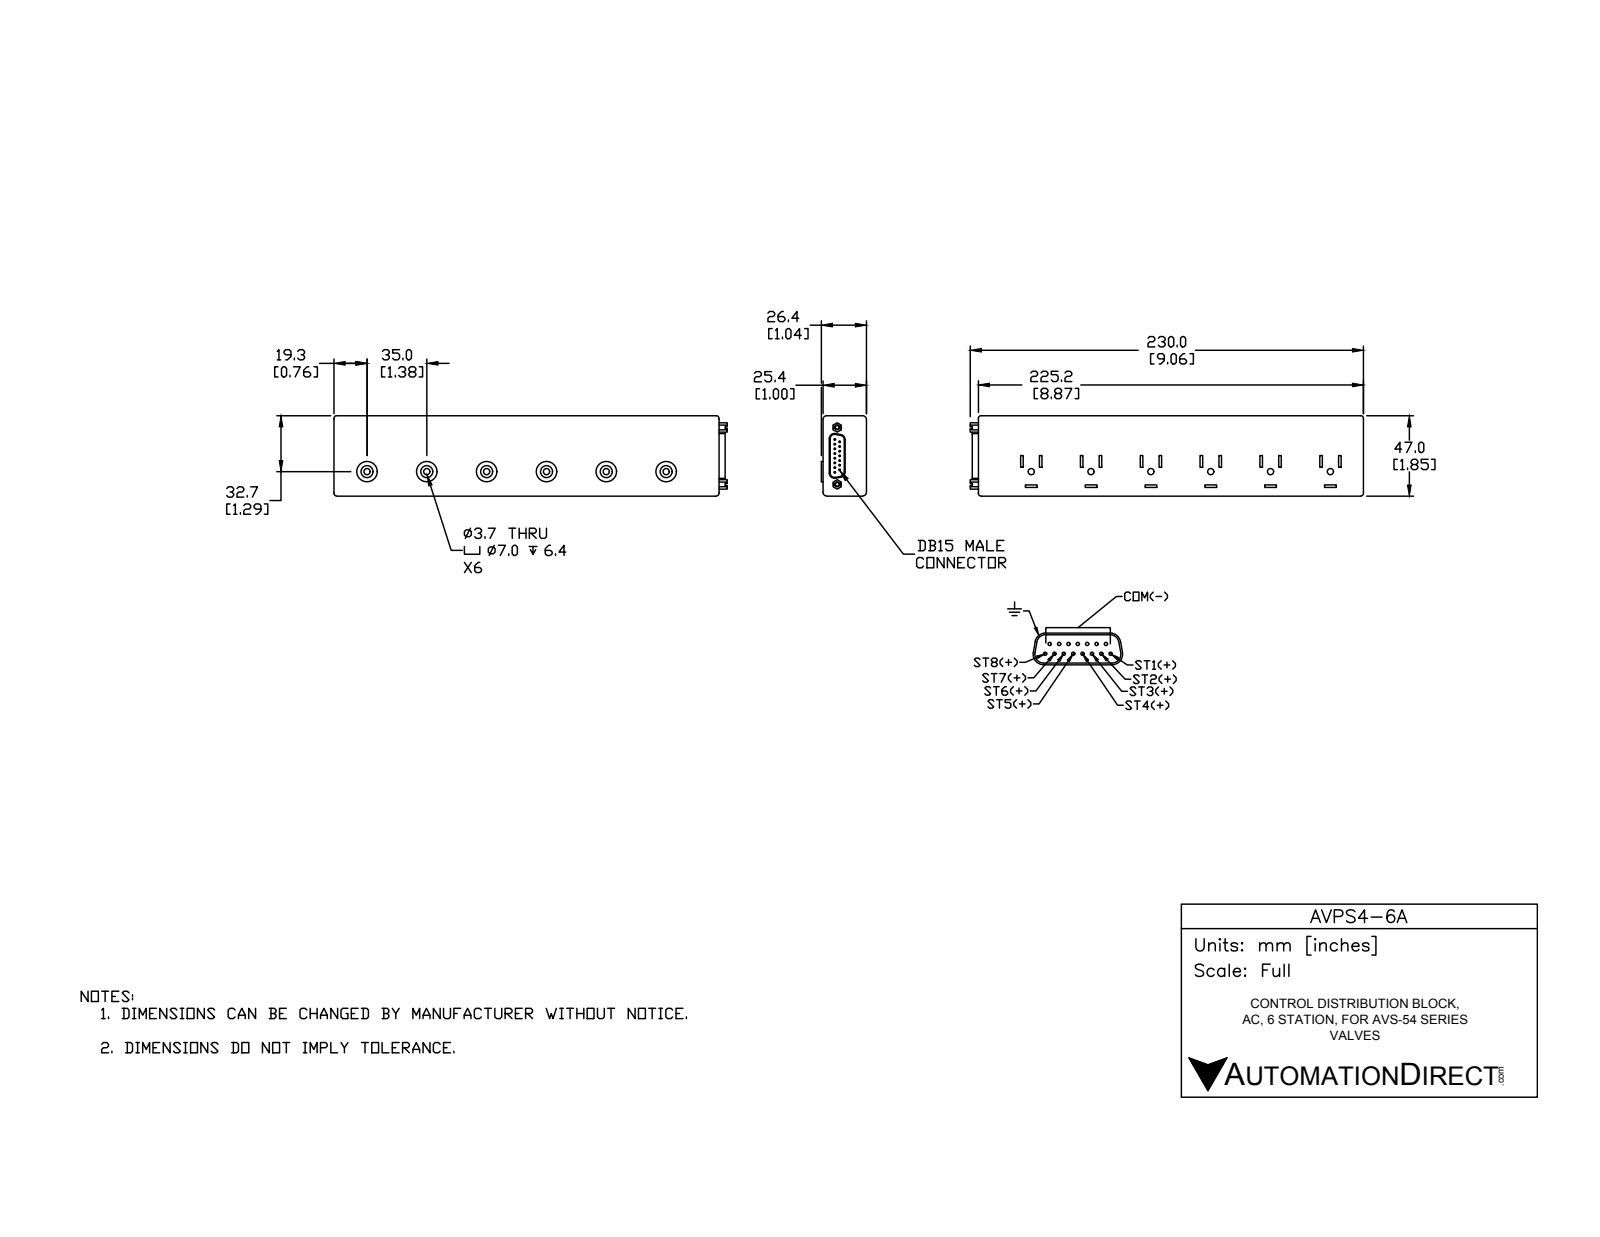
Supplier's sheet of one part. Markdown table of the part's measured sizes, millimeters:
| quantity | value |
| --- | --- |
| part name | AVPS4-6A |
| STEP written by | SolidWorks 2016 (AUTOMOTIVE_DESIGN) |
| units | millimeters |
| bodies | 1 solid, 265 faces (161 planar, 92 cylindrical, 12 other) |
| overall size | 230 × 47 × 26.4 |
| volume | 264 200 mm³ |
| surface area | 39 280 mm² |
| round holes (diameter × count) | 3.7 × 6, 7 × 6, 2.3 × 2 |
| round bosses / shafts (diameter × count) | 1 × 15, 11.9 × 6 |
| partial cylindrical surfaces (radius × count) | 1.6 × 8, 2.3 × 4, 2.6 × 4, 3.1 × 4 |
| main face-to-face distances | 25.4, 47, 225.2, 1.5, 1, 26.4, 35, 6.4, 20.1, 11 |
| hole center spacings | 35, 105, 70, 70, 140, 33.3, 35, 175 |
